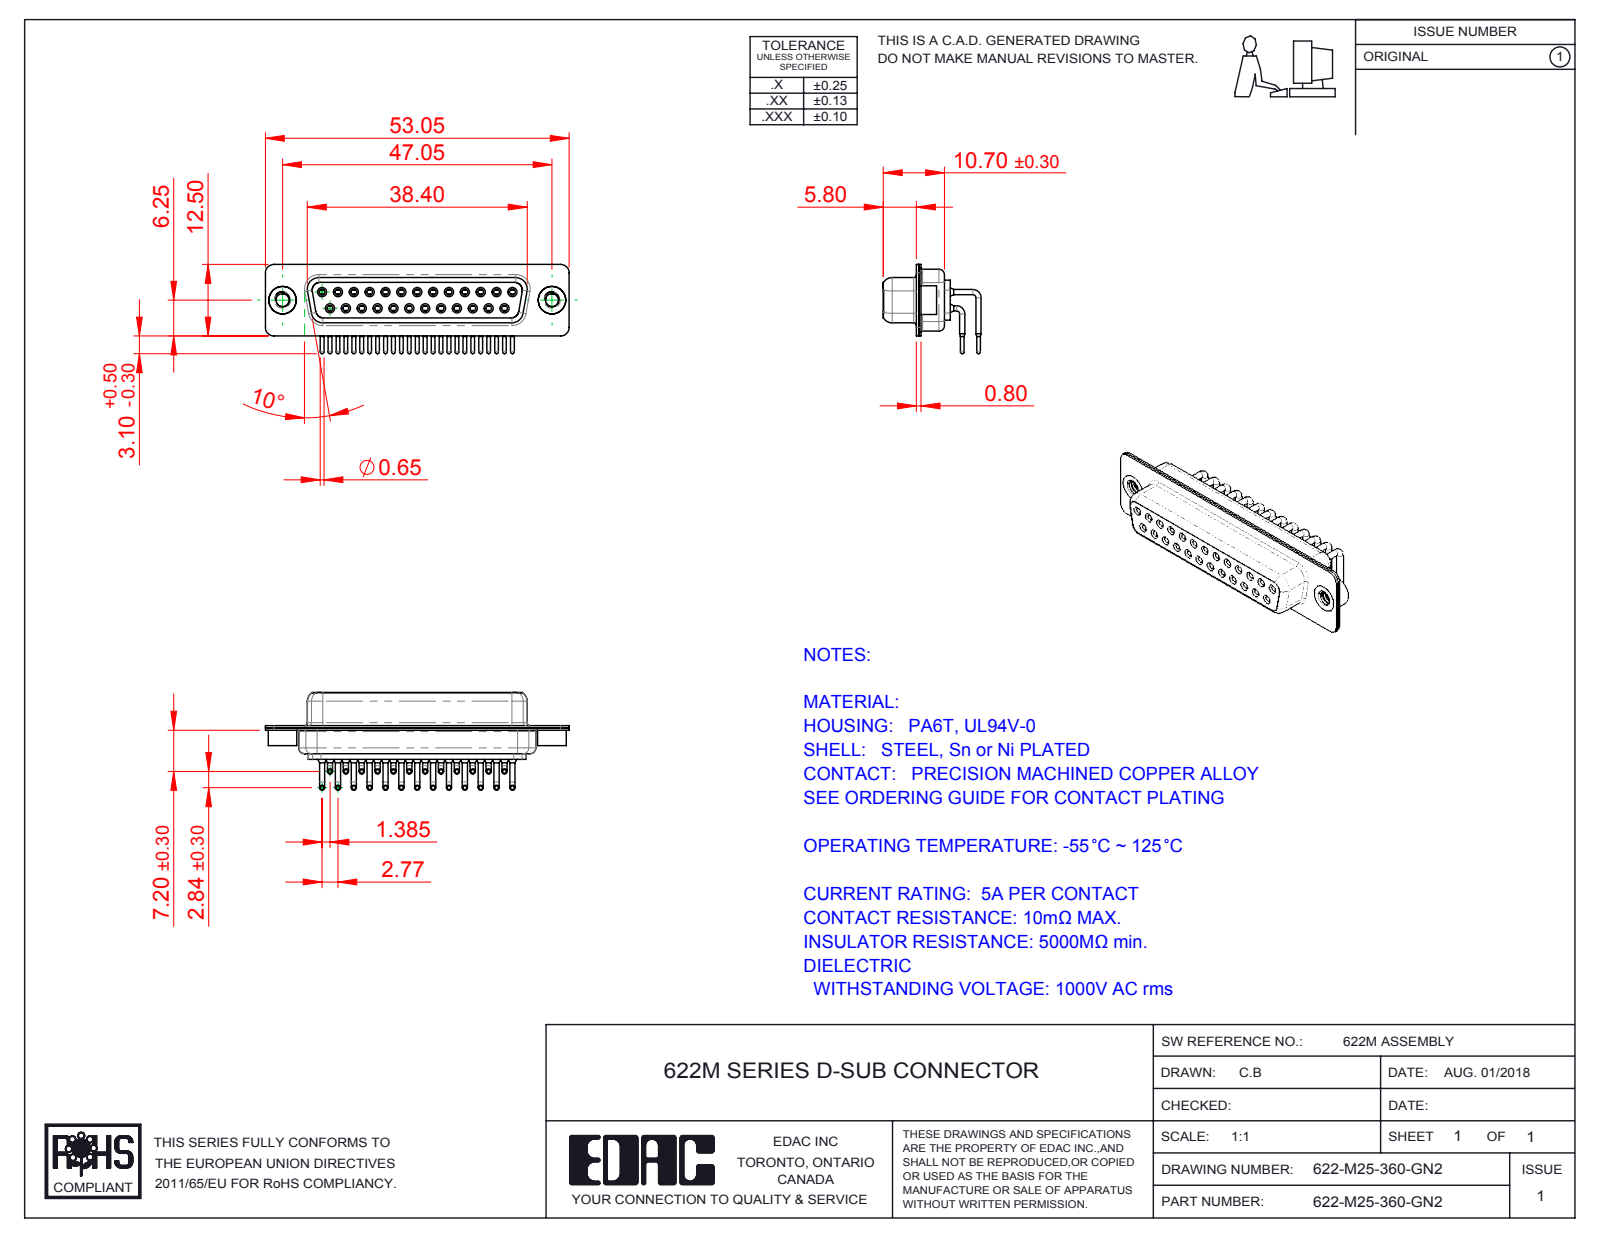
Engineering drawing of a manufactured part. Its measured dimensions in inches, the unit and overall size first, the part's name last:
Units: inches
Overall size (bounding box): 2.089 × 0.673 × 0.614
Round holes (diameter × count): ⌀0.039 ×25, ⌀0.043 ×25, ⌀0.067 ×25, ⌀0.071 ×25, ⌀0.079 ×25, ⌀0.089 ×2, ⌀0.157 ×2, ⌀0.189 ×2
Round bosses / shafts (diameter × count): ⌀0.035 ×50, ⌀0.063 ×25, ⌀0.059 ×25, ⌀0.026 ×25, ⌀0.197 ×2, ⌀0.193 ×2
Partial cylindrical surfaces — rounded edges, fillets, slot ends (radius × count): R0.059 ×16, R0.079 ×12, R0.053 ×8, R0.063 ×8, R0.01 ×4, R0.02 ×4, R0.024 ×4, R0.026 ×4
Main face-to-face distances: 0.016, 0.057, 0.352, 0.244, 0.091, 0.075, 0.335, 0.018, 0.278, 0.033
Hole centre spacings: 0.124, 0.109, 0.218, 0.327, 0.436, 0.545, 0.654, 0.198
Volume: 0.235 in³ · Surface area: 14.73 in²
Bodies: 30 solids, 1604 faces (442 planar, 712 cylindrical, 450 other)
Part name (STEP PRODUCT): 622M Contact Row 1; 622M Shell Front_25 Contacts; 622-M25-360-GN2; 622M Housing_25 Contacts (+3 more)
STEP written by: SolidWorks 2016 (CONFIG_CONTROL_DESIGN)
